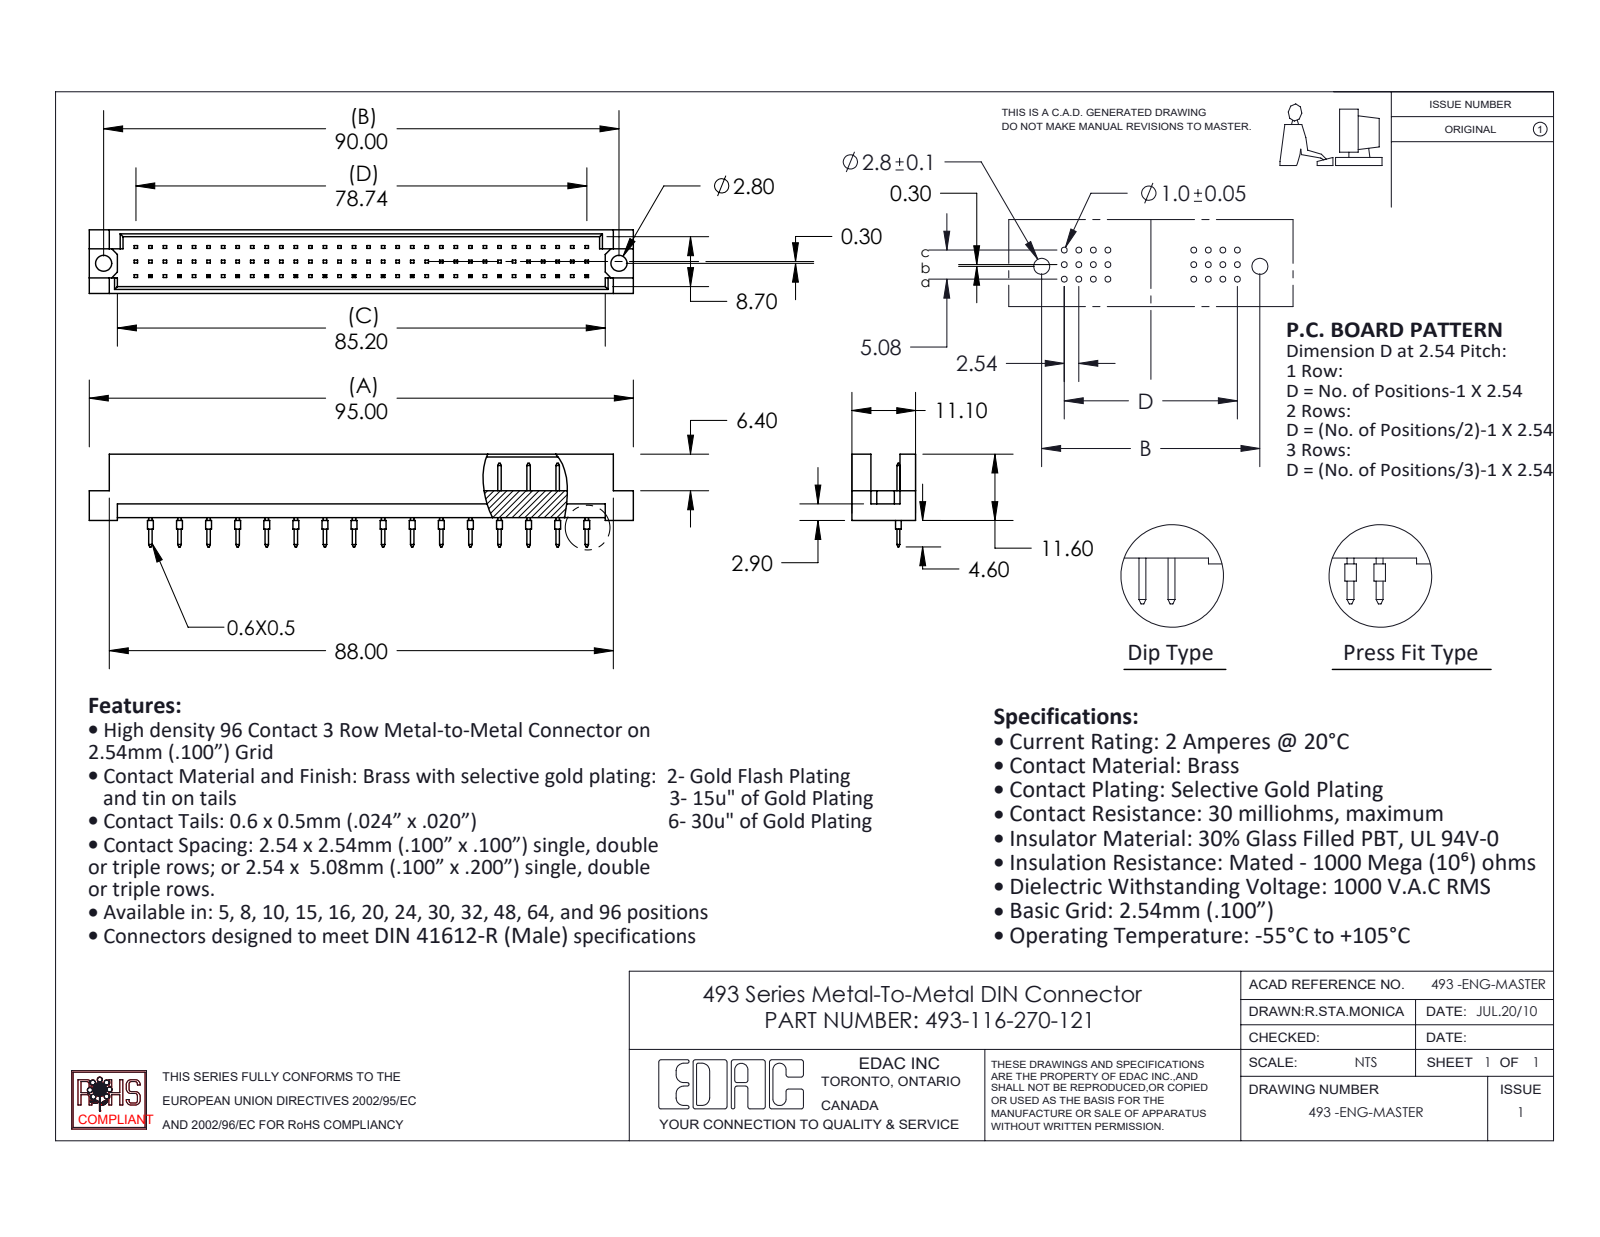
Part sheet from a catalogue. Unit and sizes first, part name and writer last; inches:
Units: inches
Overall size (bounding box): 3.74 × 0.638 × 0.437
Round holes (diameter × count): ⌀0.11 ×2
Round bosses / shafts (diameter × count): ⌀0.039 ×16
Main face-to-face distances: 0.047, 0.39, 0.437, 0.343, 0.185, 0.02, 0.2, 0.1, 0.109, 0.128
Hole centre spacings: 3.543
Volume: 0.35 in³ · Surface area: 10.88 in²
Bodies: 17 solids, 788 faces (752 planar, 36 cylindrical, 0 other)
Part name (STEP PRODUCT): 493-290_70; 493-116-270-121; 493 Part_96
STEP written by: SolidWorks 2020 (CONFIG_CONTROL_DESIGN)
